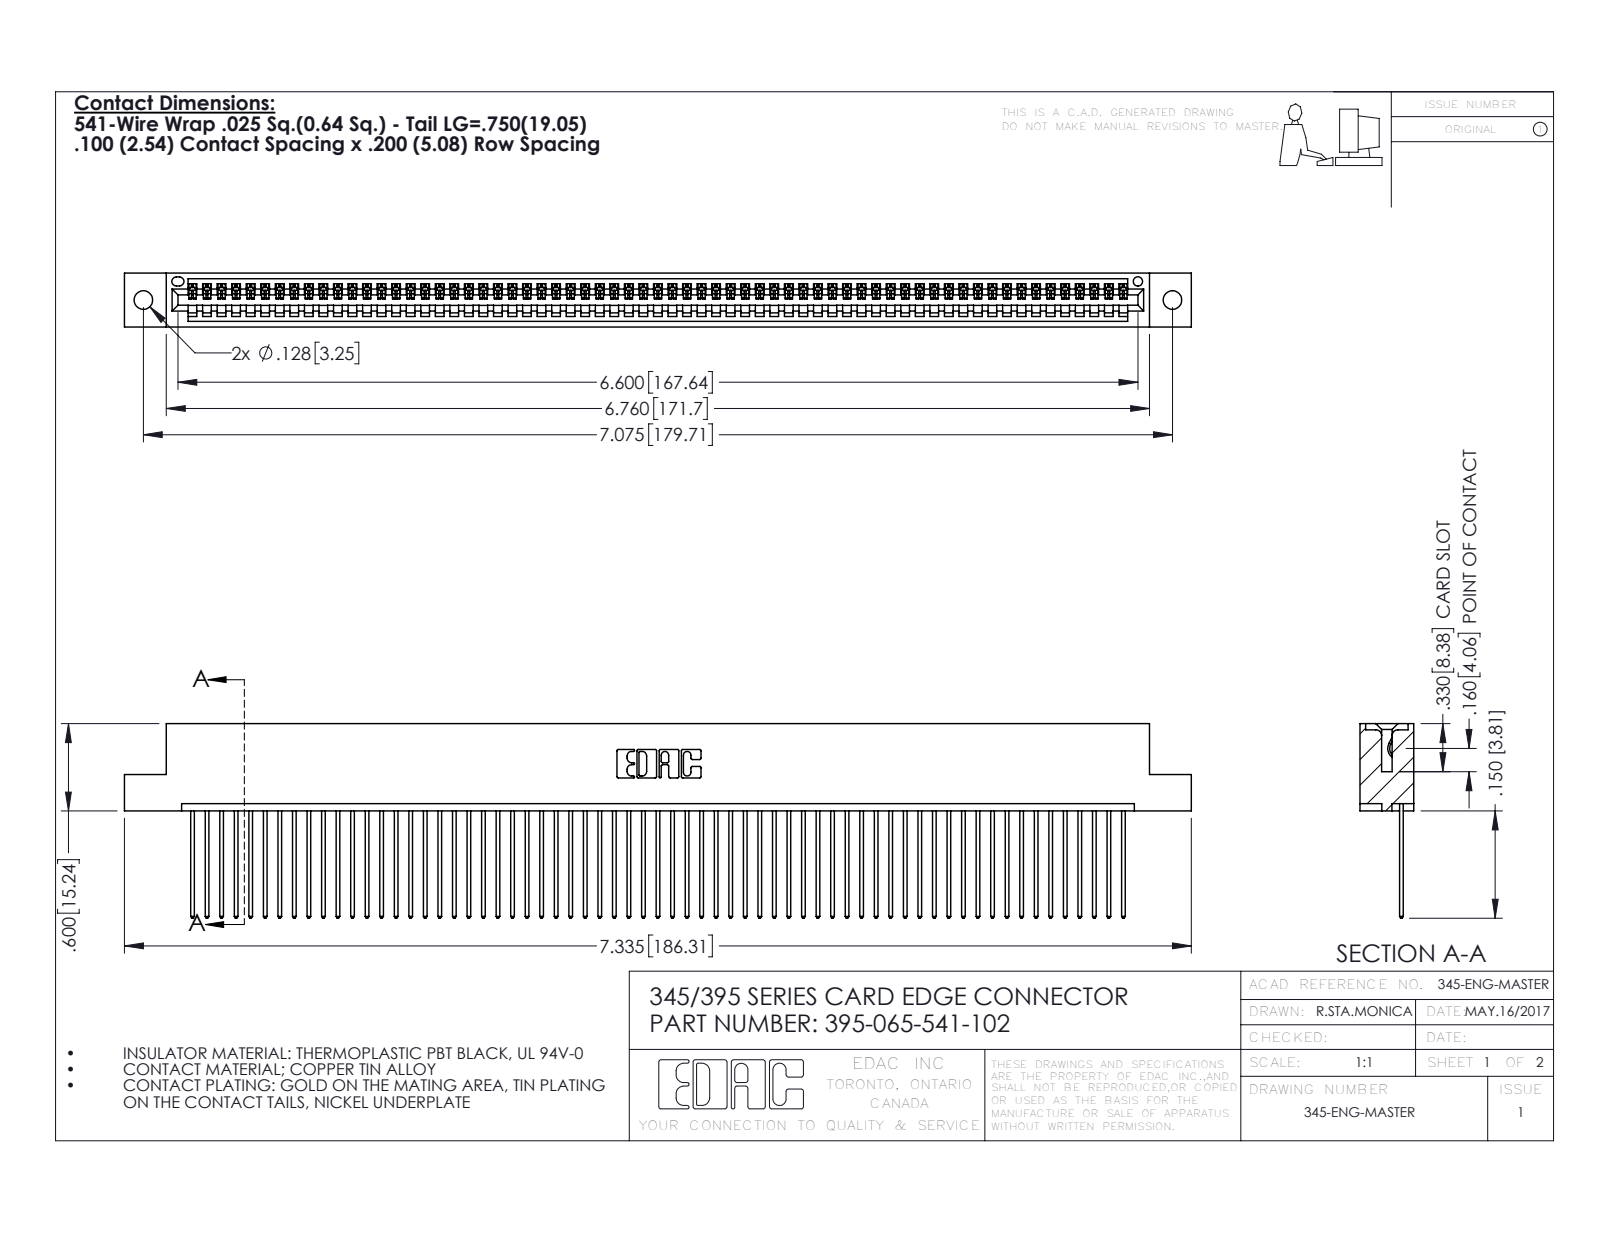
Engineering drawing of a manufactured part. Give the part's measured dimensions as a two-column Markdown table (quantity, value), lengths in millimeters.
| quantity | value |
| --- | --- |
| part name | 395-065-541-102; 345-292-001_345-293-141; 345 Part_Flush Mounting Lugs - 0.128 Dia |
| STEP written by | SolidWorks 2016 (CONFIG_CONTROL_DESIGN) |
| units | millimeters |
| bodies | 66 solids, 3896 faces (2680 planar, 1216 cylindrical, 0 other) |
| overall size | 186.3 × 34 × 9.4 |
| volume | 18 060 mm³ |
| surface area | 25 300 mm² |
| round holes (diameter × count) | 3.3 × 2, 1.6 × 1 |
| partial cylindrical surfaces (radius × count) | 0.2 × 130, 0.3 × 130, 0.3 × 22, 0.2 × 6, 0.8 × 6, 0.7 × 3, 0.8 × 2, 1 × 2 |
| main face-to-face distances | 1.8, 7.6, 2.5, 6.9, 0.6, 9.4, 5.1, 5.7, 3.8, 1.8 |
| hole center spacings | 6.9, 173.7, 179.7 |
